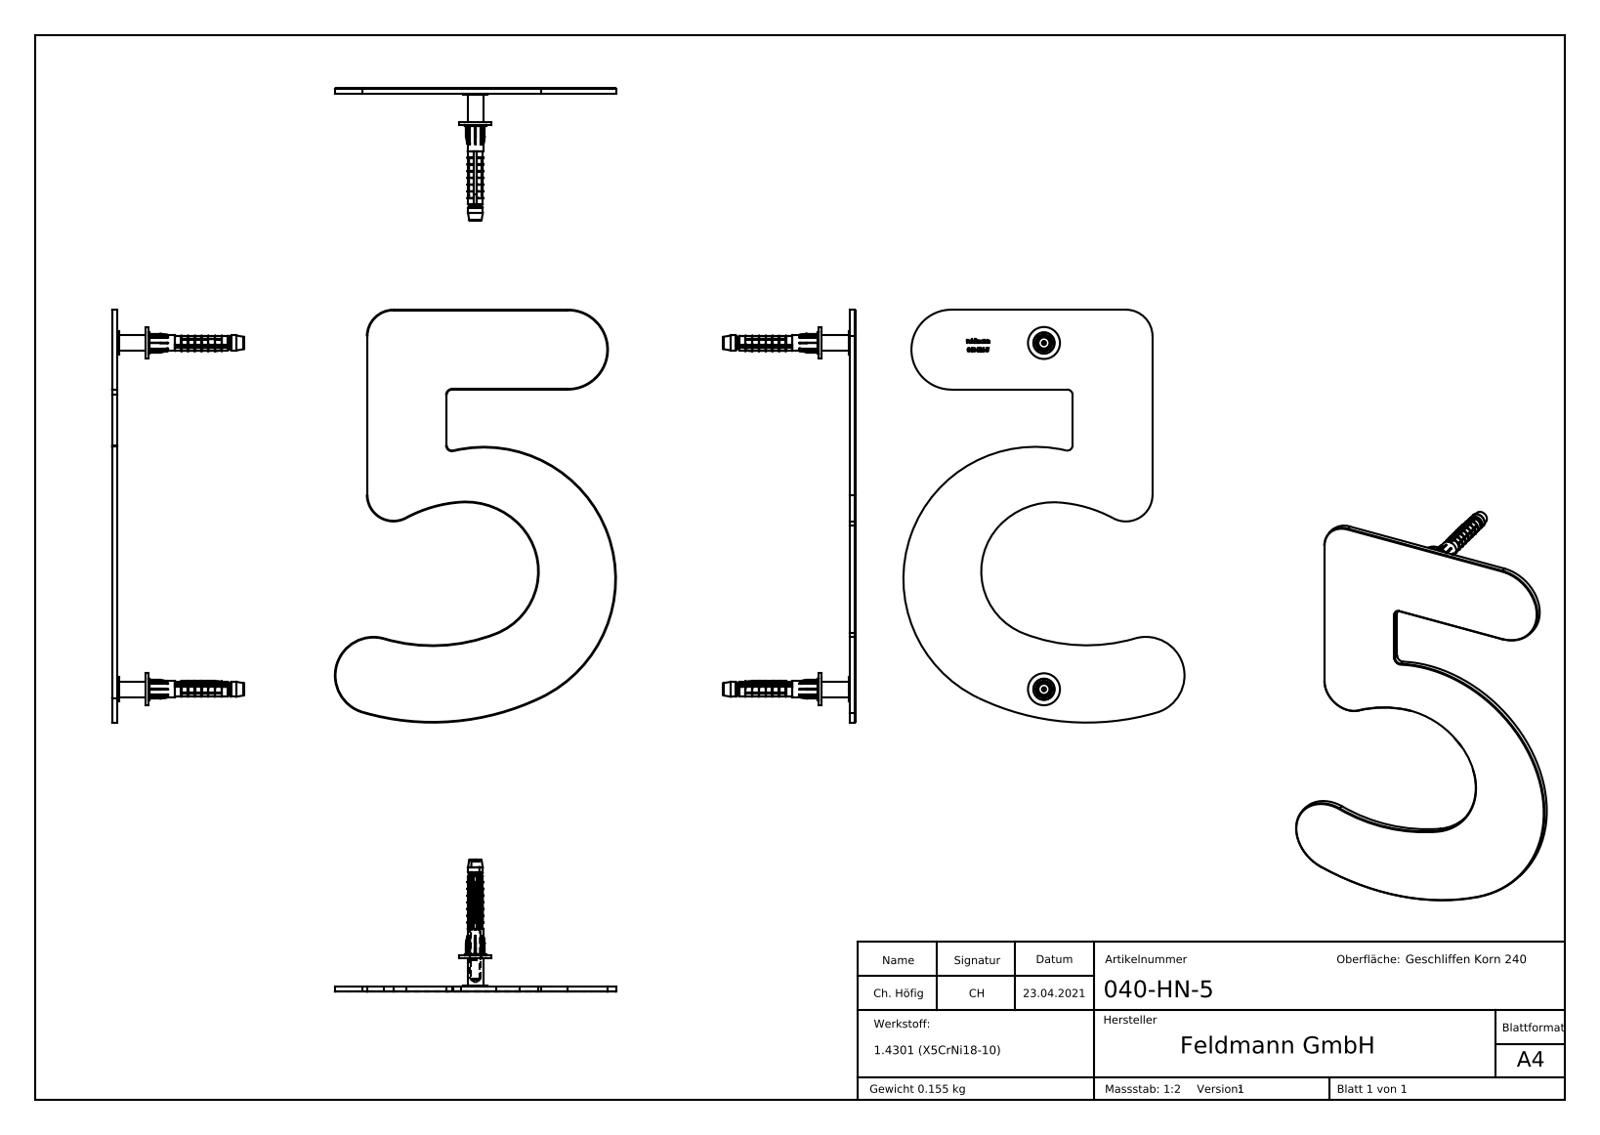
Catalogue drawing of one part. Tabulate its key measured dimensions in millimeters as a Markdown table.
| quantity | value |
| --- | --- |
| part name | 040-HN-5; 040-HN-X Teil2_040-HN-X Teil2; 040-HN-X Teil4; 040-HN-X Teil3 (+5 more) |
| STEP written by | SolidWorks 2018 (CONFIG_CONTROL_DESIGN) |
| units | millimeters |
| bodies | 7 solids, 1571 faces (361 planar, 395 cylindrical, 815 other) |
| overall size | 10000 × 5217.43 × 4607.88 |
| volume | 20 574 mm³ |
| surface area | 23 587 mm² |
| round holes (diameter × count) | 3.3 × 2, 4.3 × 2 |
| round bosses / shafts (diameter × count) | 12 × 2, 9 × 2, 8 × 2, 6 × 2, 5.8 × 2, 5.6 × 2, 4.6 × 2, 4 × 2 |
| partial cylindrical surfaces (radius × count) | 0.1 × 22, 0.25 × 4, 2 × 2, 3.5 × 2, 10 × 2, 14.5 × 1, 15 × 1, 25 × 1 |
| main face-to-face distances | 2, 11.6, 13.6, 12.5, 1.1, 10.5, 30, 0.5, 2.5, 10 |
| hole center spacings | 130 |
